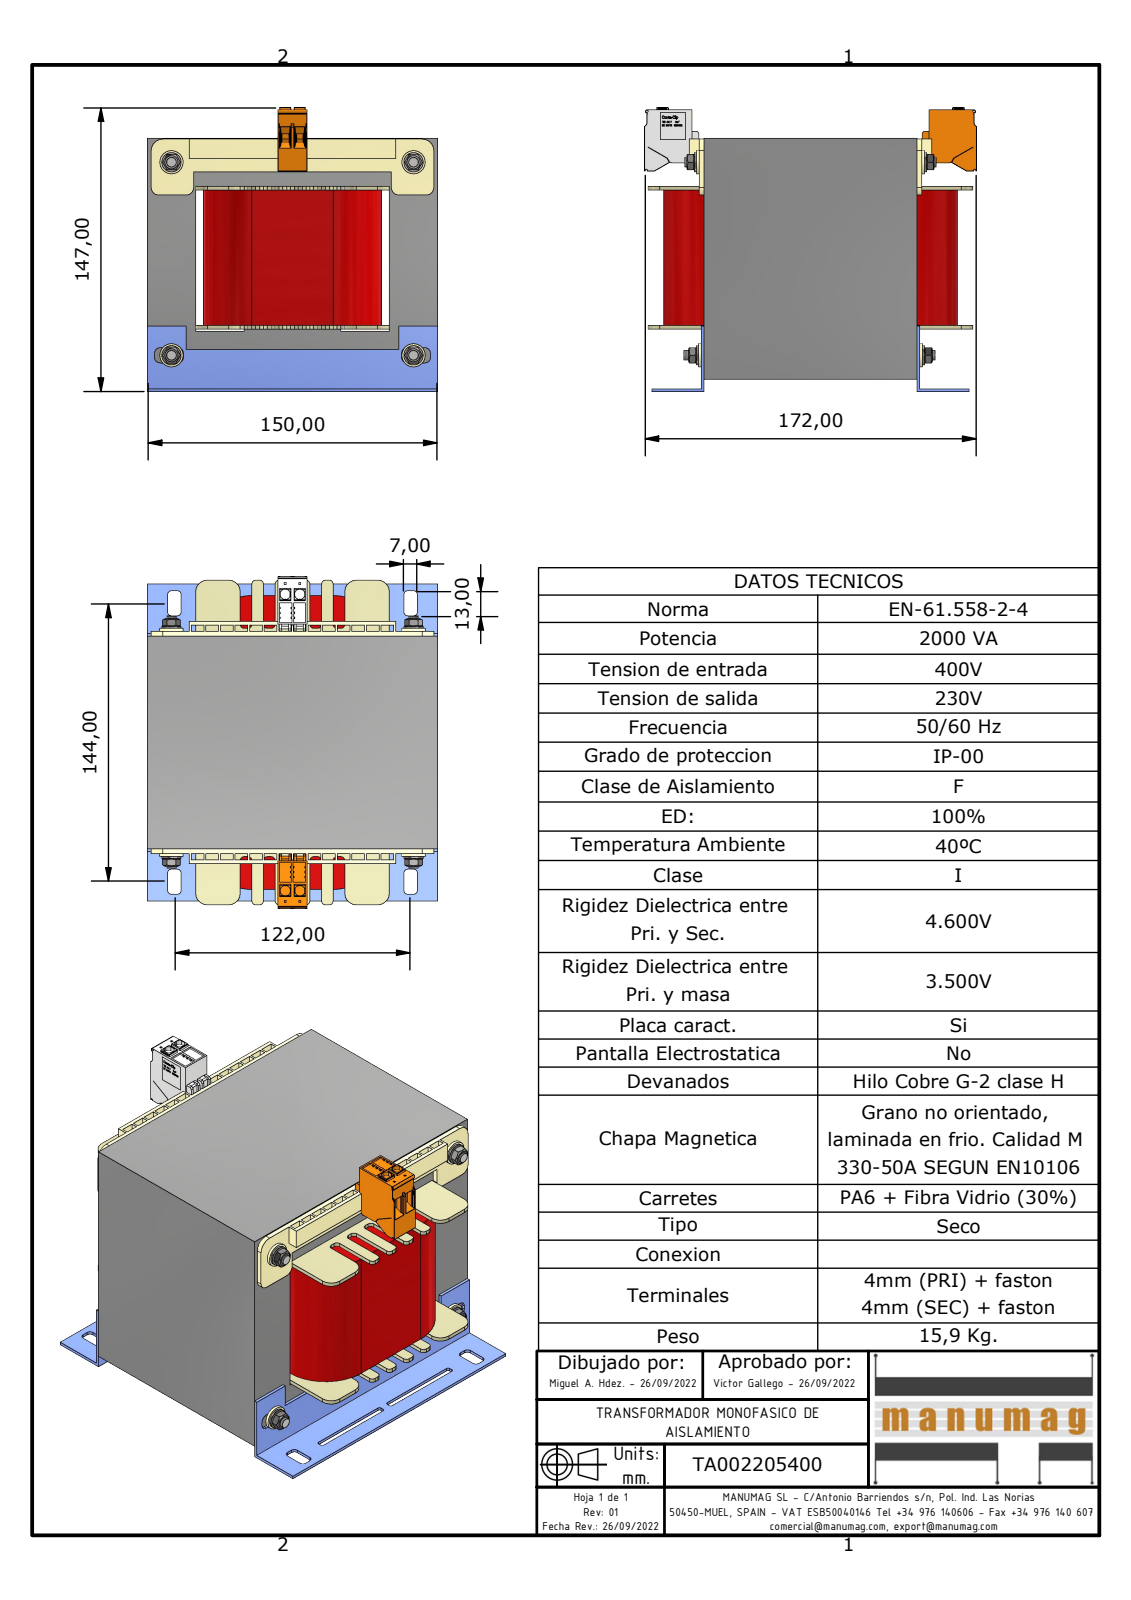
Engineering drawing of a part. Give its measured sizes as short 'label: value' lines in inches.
name: TA002205400; EI150 x 125 - 110 (RC50); AF50DIN; EI150 (+7 more)
written by: Autodesk Inventor 2023 (AUTOMOTIVE_DESIGN)
unit: in
bodies: 36 solids, 3990 faces (3196 planar, 566 cylindrical, 228 other)
size: 6.768 × 5.906 × 5.803
volume: 140 in³; area: 478.8 in²
holes: 4× ⌀0.163, 4× ⌀0.197, 4× ⌀0.209, 4× ⌀0.315
bosses: 4× ⌀0.472, 4× ⌀0.394, 4× ⌀0.232
rounds: 164× R0.006, 60× R0.008, 52× R0.079, 24× R0.039, 16× R0.02, 12× R0.012, 10× R0.236, 8× R0.118
face distances: 3.937, 0.984, 1.969, 4.921, 4.331, 2.953, 0.059, 5.906, 0.827, 0.039
hole spacings: 3.937, 4.921, 6.302
